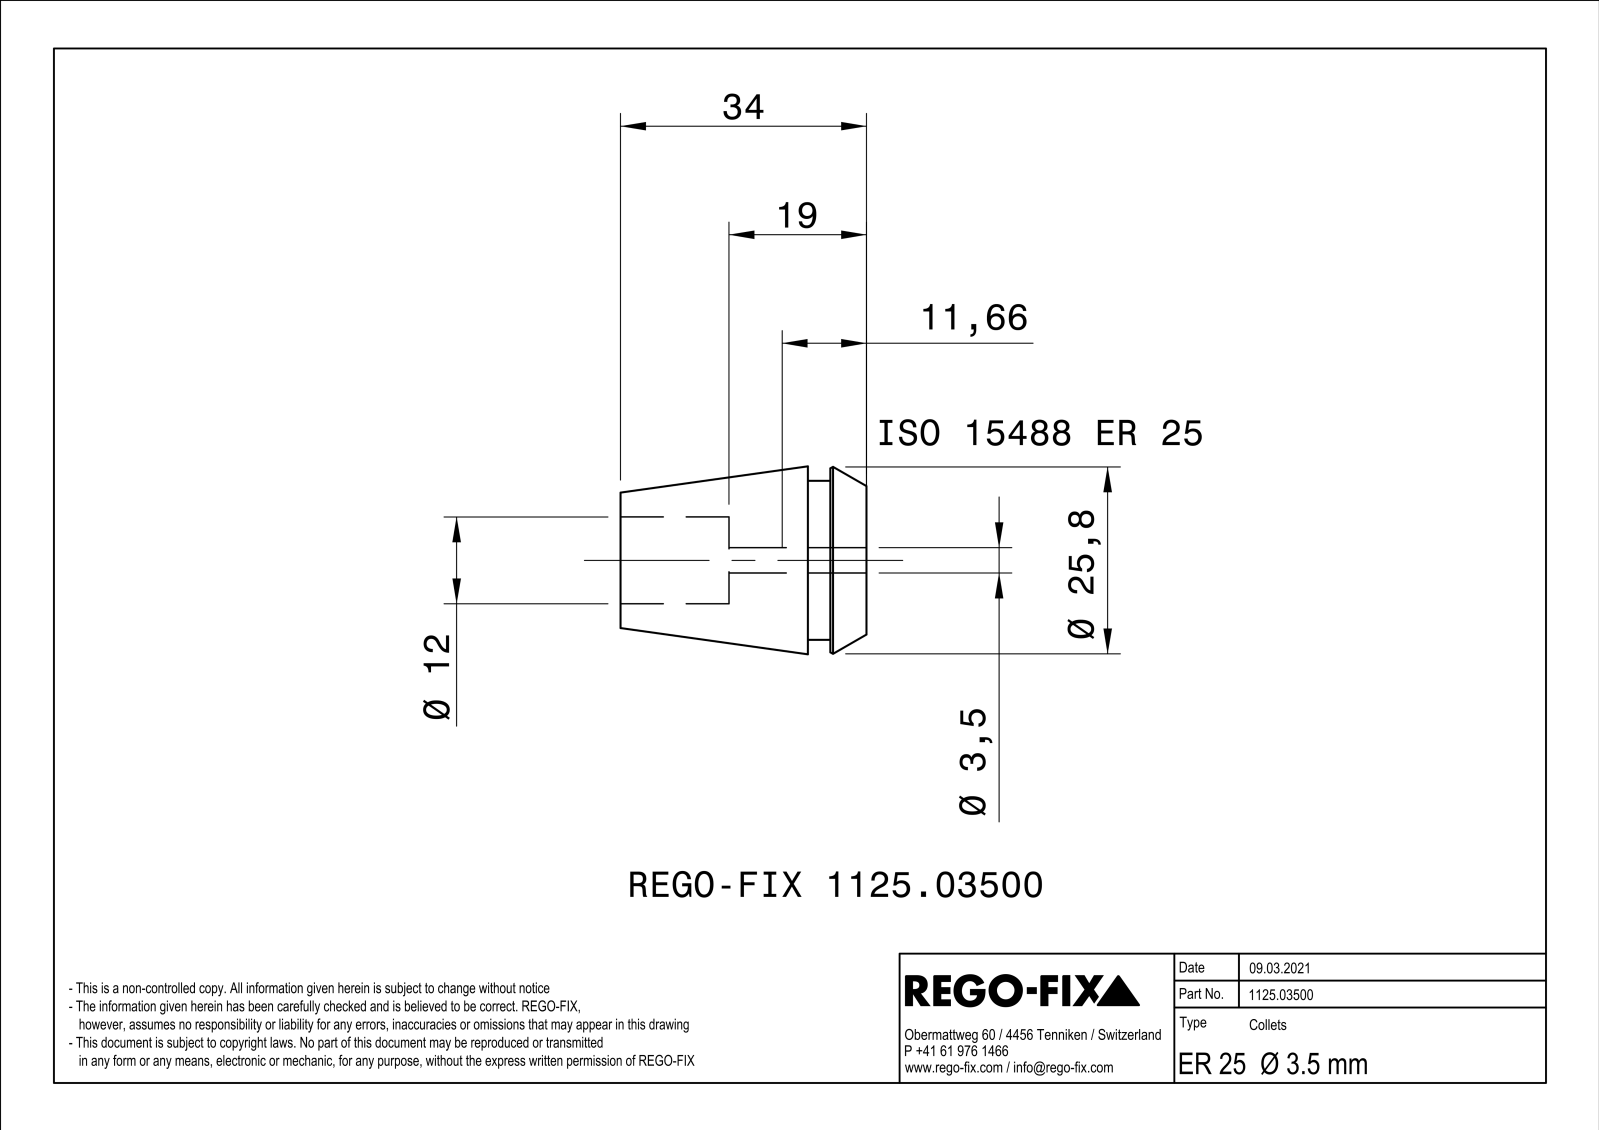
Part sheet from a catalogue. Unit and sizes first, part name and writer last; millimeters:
Units: millimetres
Overall size (bounding box): 34 × 25.99 × 25.99
Round holes (diameter × count): ⌀12 ×1
Round bosses / shafts (diameter × count): ⌀22 ×1
Partial cylindrical surfaces — rounded edges, fillets, slot ends (radius × count): R40 ×8, R1.75 ×1
Main face-to-face distances: 0.6, 0.62, 0.58, 8.1, 34, 25.9, 5, 3.1, 29, 19
Volume: 9 944 mm³ · Surface area: 9 429 mm²
Bodies: 1 solid, 272 faces (104 planar, 48 cylindrical, 120 other)
Part name (STEP PRODUCT): NOCUT
STEP written by: SIEMENS PLM Software Solid Edge ST10 (AUTOMOTIVE_DESIGN)
